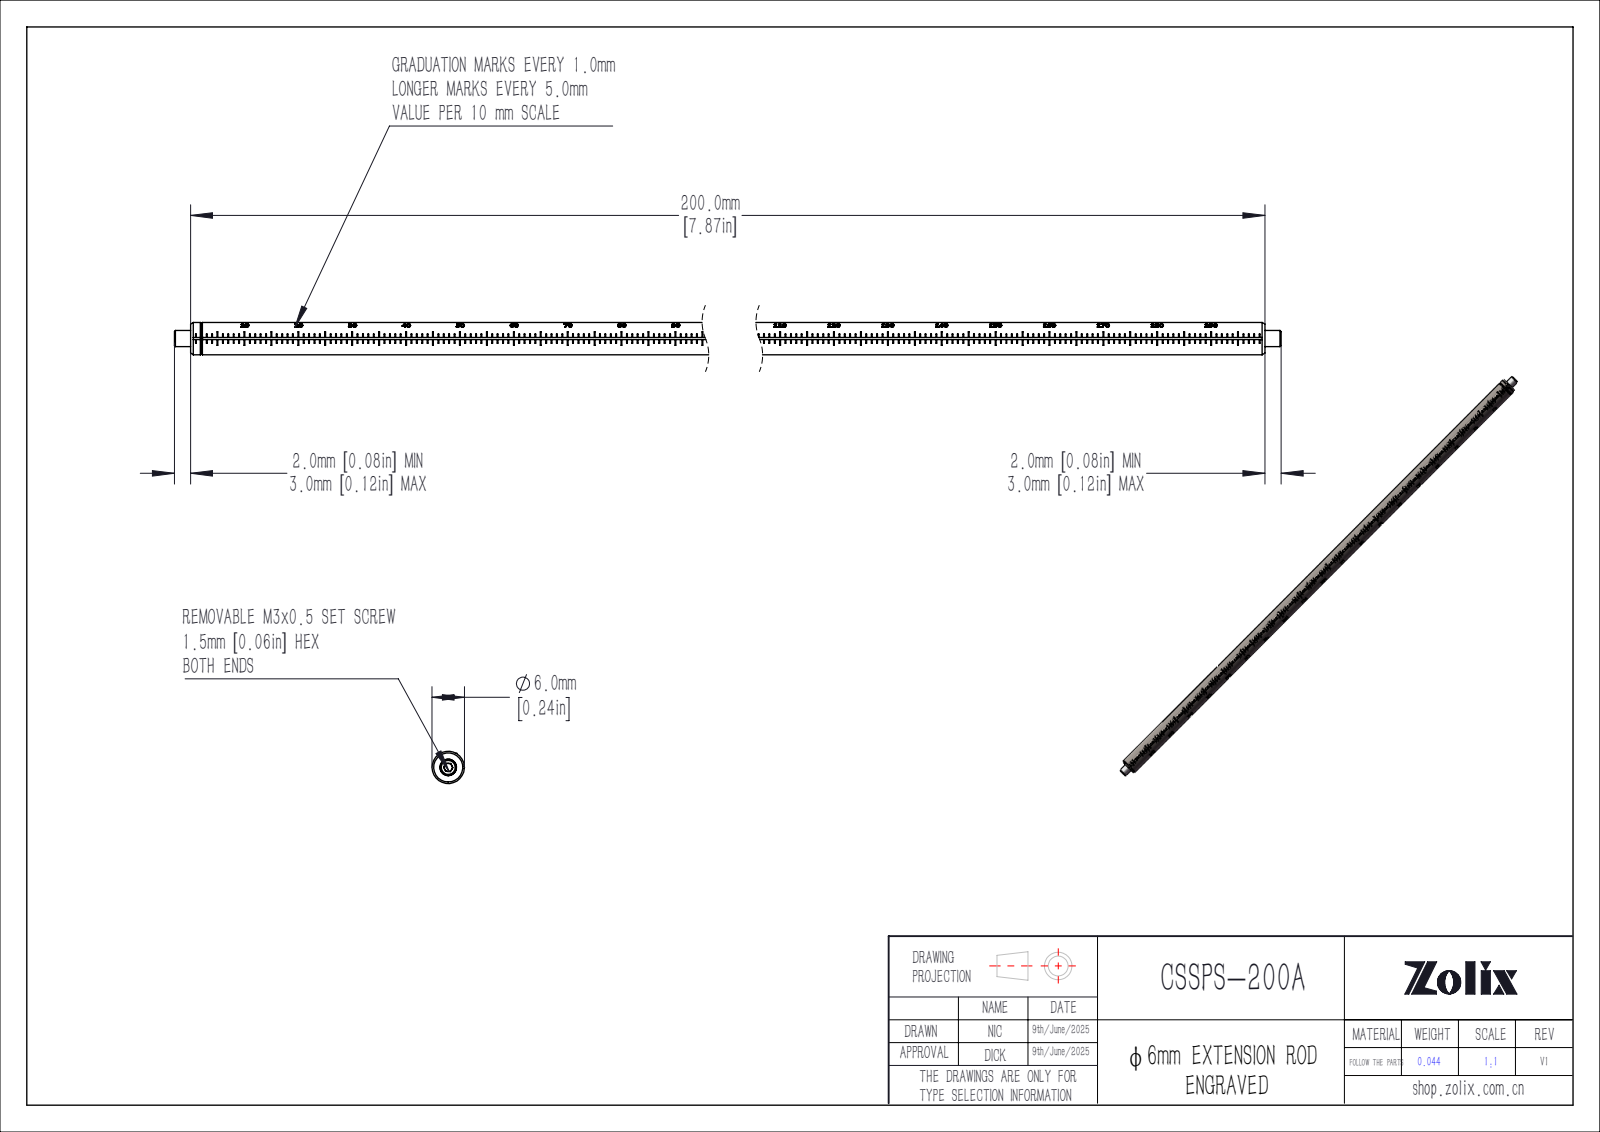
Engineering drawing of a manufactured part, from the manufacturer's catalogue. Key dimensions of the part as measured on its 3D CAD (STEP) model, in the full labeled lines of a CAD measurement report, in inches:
Part name (STEP PRODUCT): 内六角凹端紧定螺钉M3×6; CSSPS-200A
STEP written by: SolidWorks 2023 (CONFIG_CONTROL_DESIGN)
Units: inches
Bodies: 3 solids, 2328 faces (1718 planar, 94 cylindrical, 516 other)
Overall size (bounding box): 8.11 × 0.236 × 0.236
Volume: 0.346 in³ · Surface area: 6.268 in²
Round holes (diameter × count): ⌀0.098 ×1
Round bosses / shafts (diameter × count): ⌀0.236 ×1, ⌀0.118 ×1
Partial cylindrical surfaces — rounded edges, fillets, slot ends (radius × count): R0.118 ×1
Main face-to-face distances: 7.874, 0.118, 7.992, 0.059, 8.11, 0.059, 0.016, 0.041, 0.026, 0.047
